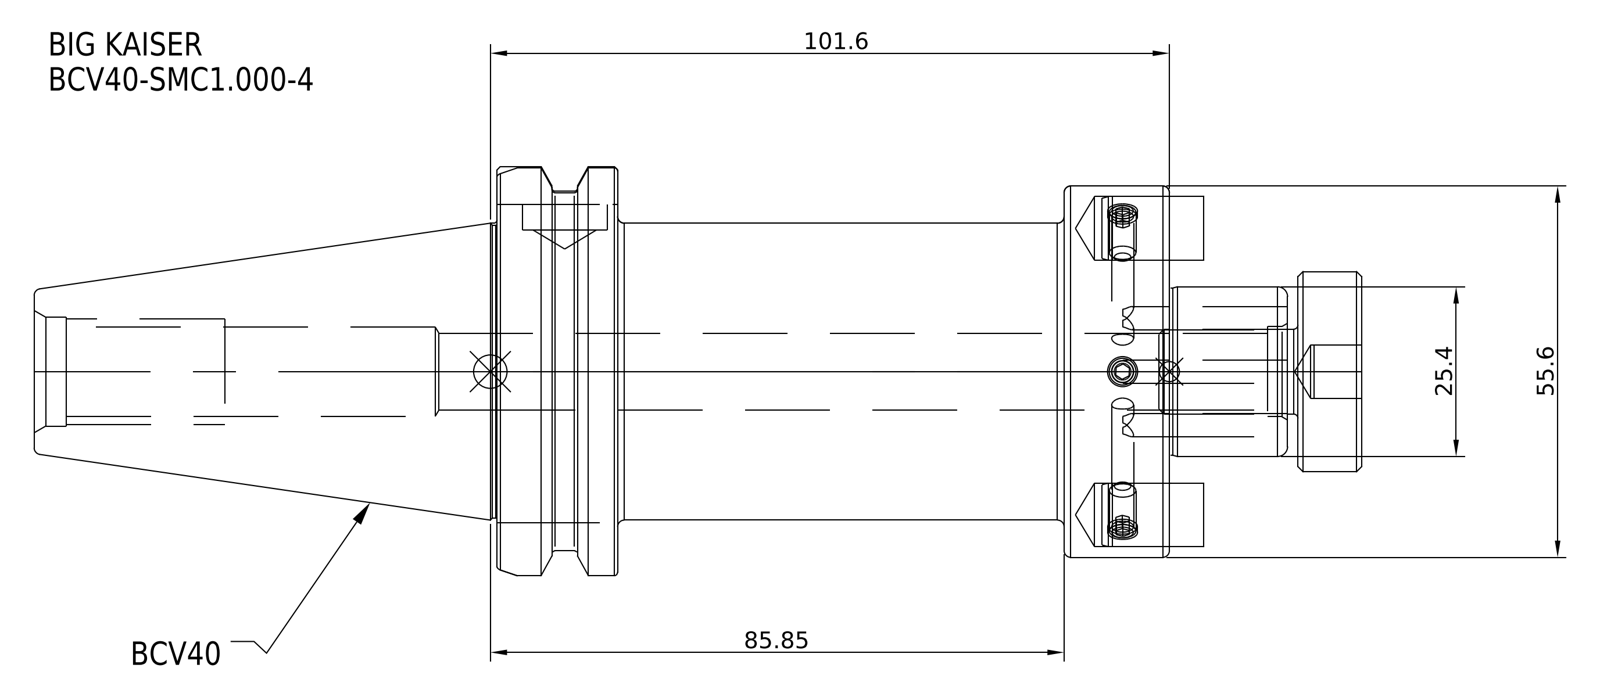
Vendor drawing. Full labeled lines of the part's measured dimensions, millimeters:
Part name (STEP PRODUCT): BCV40-SMC1_000-4
STEP written by: SolidWorks 2021 (CONFIG_CONTROL_DESIGN)
Units: millimetres
Bodies: 1 solid, 38 faces (18 planar, 14 cylindrical, 6 other)
Overall size (bounding box): 174.75 × 63.5 × 63.5
Volume: 256 693 mm³ · Surface area: 33 865 mm²
Round holes (diameter × count): ⌀11.51 ×1
Round bosses / shafts (diameter × count): ⌀63.5 ×1, ⌀56.36 ×1, ⌀55.6 ×1, ⌀44.45 ×1
Main face-to-face distances: 100.6, 82.55, 18.05, 15.75, 66.8, 84.85, 169.85, 154.1, 87.3, 69.25
